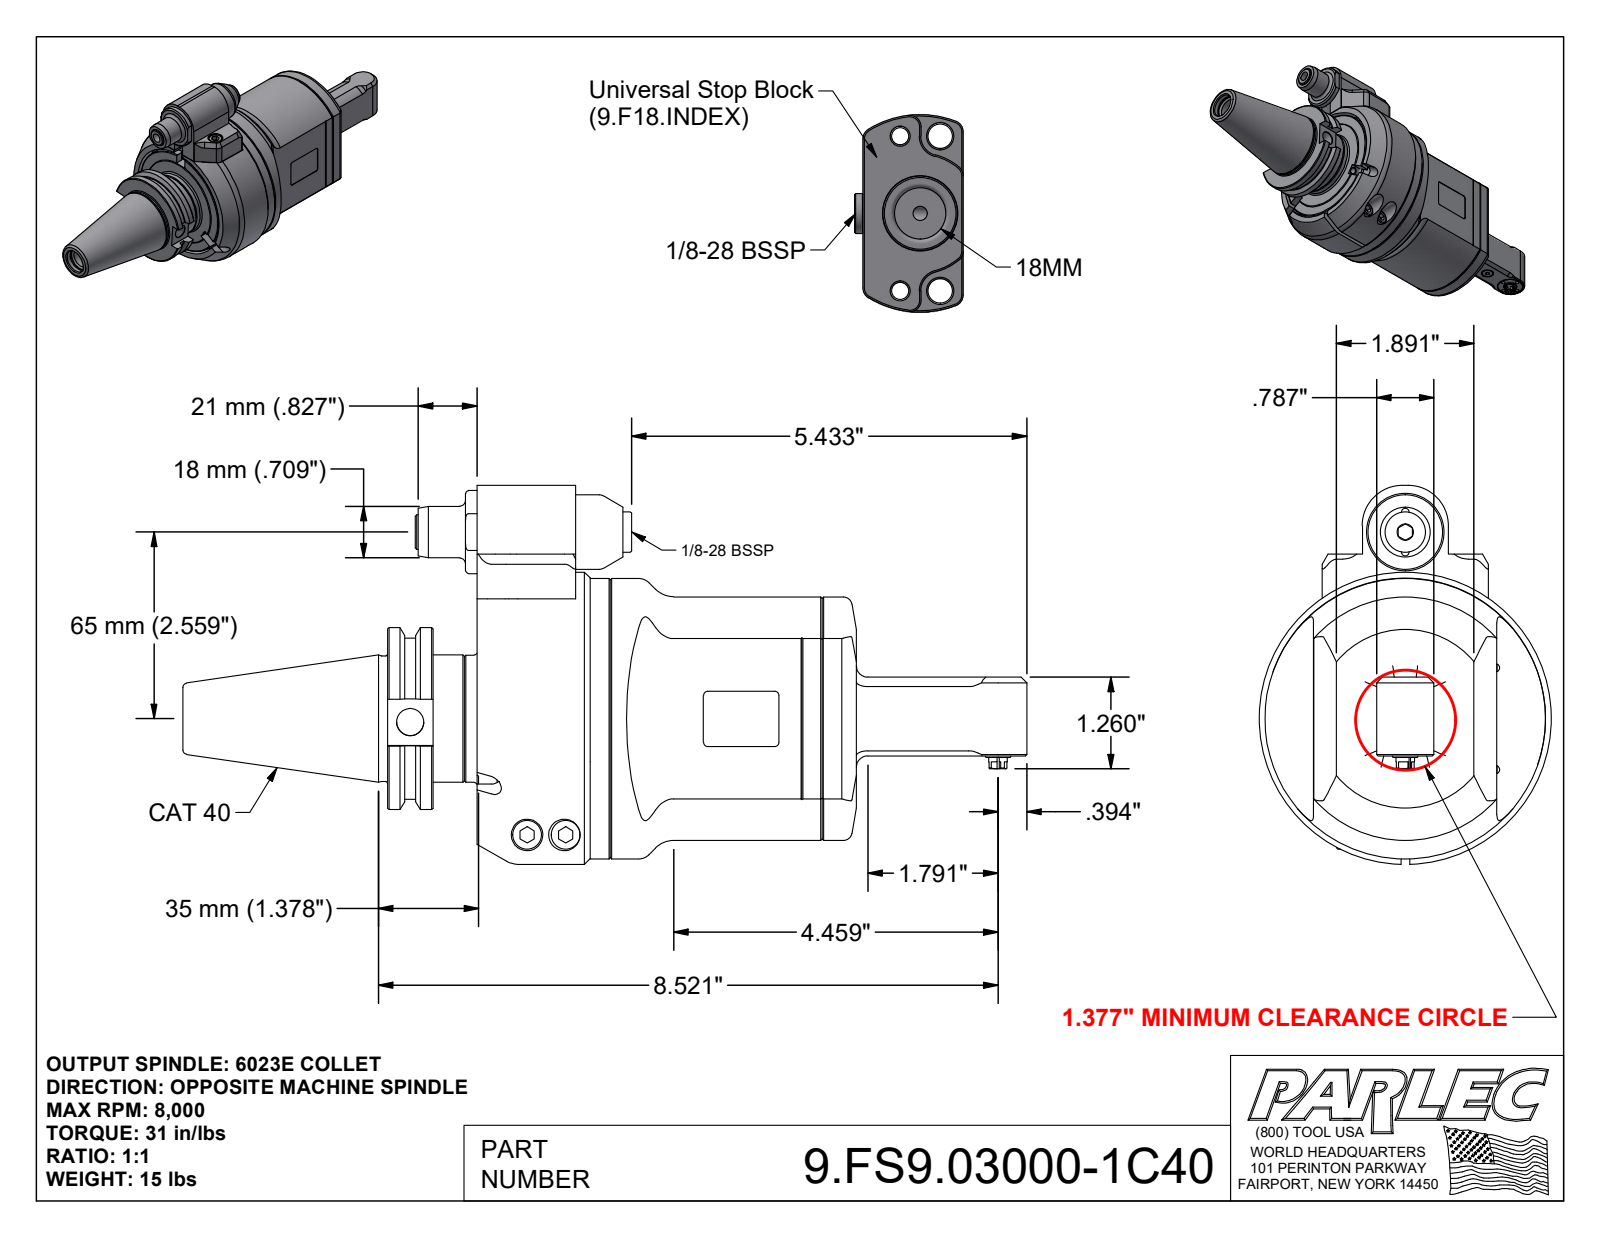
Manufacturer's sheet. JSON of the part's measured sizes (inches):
{"part_name": "9.FS9.03000-1C40; 9.FS9.03000; 9_GA1_446_2_1_C40; 9FL1ATC (+4 more)", "step_written_by": "Autodesk Inventor 2025 (AUTOMOTIVE_DESIGN)", "units": "inches", "bodies": {"solids": 5, "faces": 497, "planar": 235, "cylindrical": 129, "other": 133}, "overall_size": [11.564, 5.206, 4.016], "volume_in3": 60.39, "surface_area_in2": 215.4, "round_holes": [[0.102, 6], [0.118, 2], [0.165, 2], [0.197, 2], [0.335, 2], [0.409, 2], [0.433, 2], [0.098, 1], [0.256, 1], [0.276, 1], [0.358, 1], [0.375, 1]], "round_bosses_or_shafts": [[0.394, 4], [0.236, 4], [0.315, 3], [0.098, 2], [4.016, 1], [3.858, 1], [3.85, 1], [3.031, 1]], "partial_cylinders_radius": [[0.157, 10], [0.079, 8], [0.059, 4], [0.02, 2], [0.039, 2], [0.138, 2], [0.197, 2], [0.551, 2]], "face_to_face_distances": [0.04, 0.02, 1.26, 0.335, 0.276, 2.52, 0.295, 1.22, 0.866, 1.654], "hole_center_spacings": [0.266, 0.376, 0.276, 0.531, 0.924, 3.337, 0.512, 0.551]}
